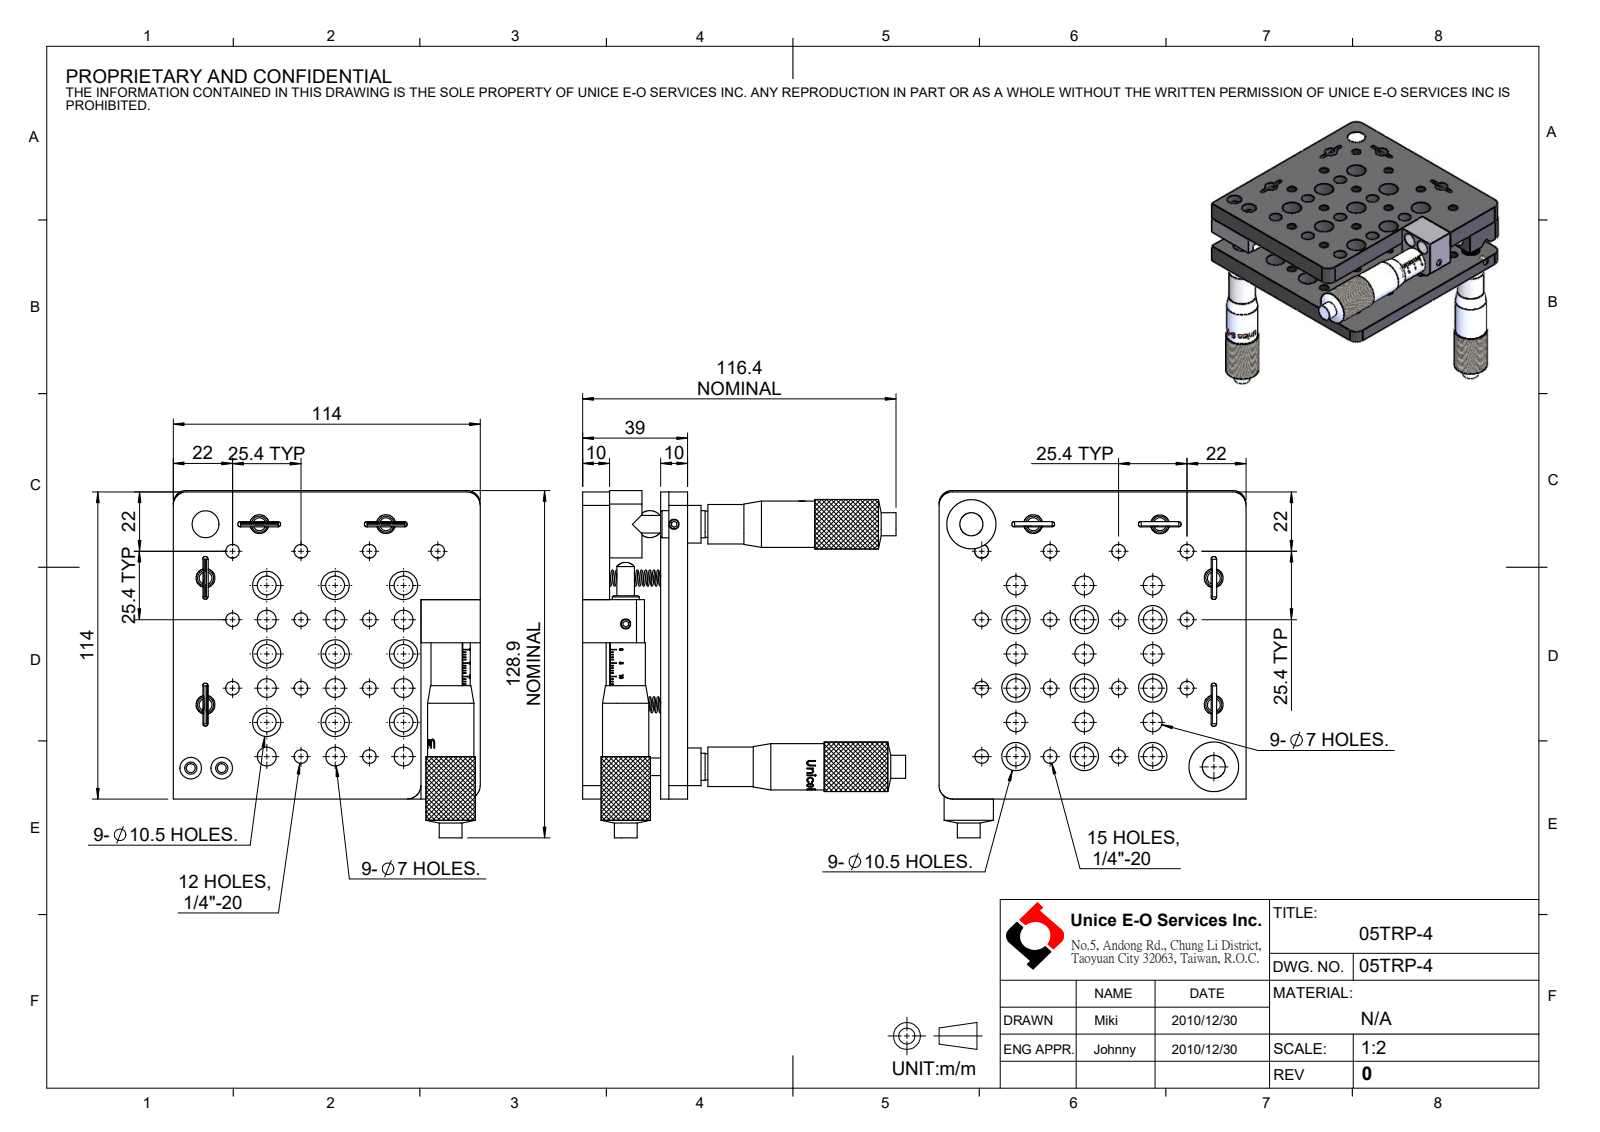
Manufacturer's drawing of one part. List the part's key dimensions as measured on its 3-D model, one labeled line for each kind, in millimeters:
Part name (STEP PRODUCT): 05TRP-4
STEP written by: SolidWorks 2016 (CONFIG_CONTROL_DESIGN)
Units: millimetres
Bodies: 32 solids, 1780 faces (994 planar, 365 cylindrical, 421 other)
Overall size (bounding box): 128.9 × 119.88 × 114
Volume: 292 751 mm³ · Surface area: 120 345 mm²
Round holes (diameter × count): ⌀7 ×23, ⌀10.5 ×18, ⌀5.11 ×15, ⌀3.3 ×7, ⌀10 ×5, ⌀1.2 ×4, ⌀4.5 ×4, ⌀8 ×4, ⌀6.3 ×3, ⌀14.65 ×3, ⌀11 ×2, ⌀1.7 ×1
Round bosses / shafts (diameter × count): ⌀1.6 ×4, ⌀0.6 ×4, ⌀18.3 ×3, ⌀17.2 ×3, ⌀14.6 ×3, ⌀9.75 ×3, ⌀8.5 ×3, ⌀6.5 ×3
Partial cylindrical surfaces — rounded edges, fillets, slot ends (radius × count): R1 ×8, R5 ×6, R8.55 ×3
Main face-to-face distances: 10, 29, 39, 19, 22, 7, 114, 12, 16, 3
Hole centre spacings: 28.4, 25.4, 40.16, 17.96, 56.8, 12.7, 35.92, 45.79
